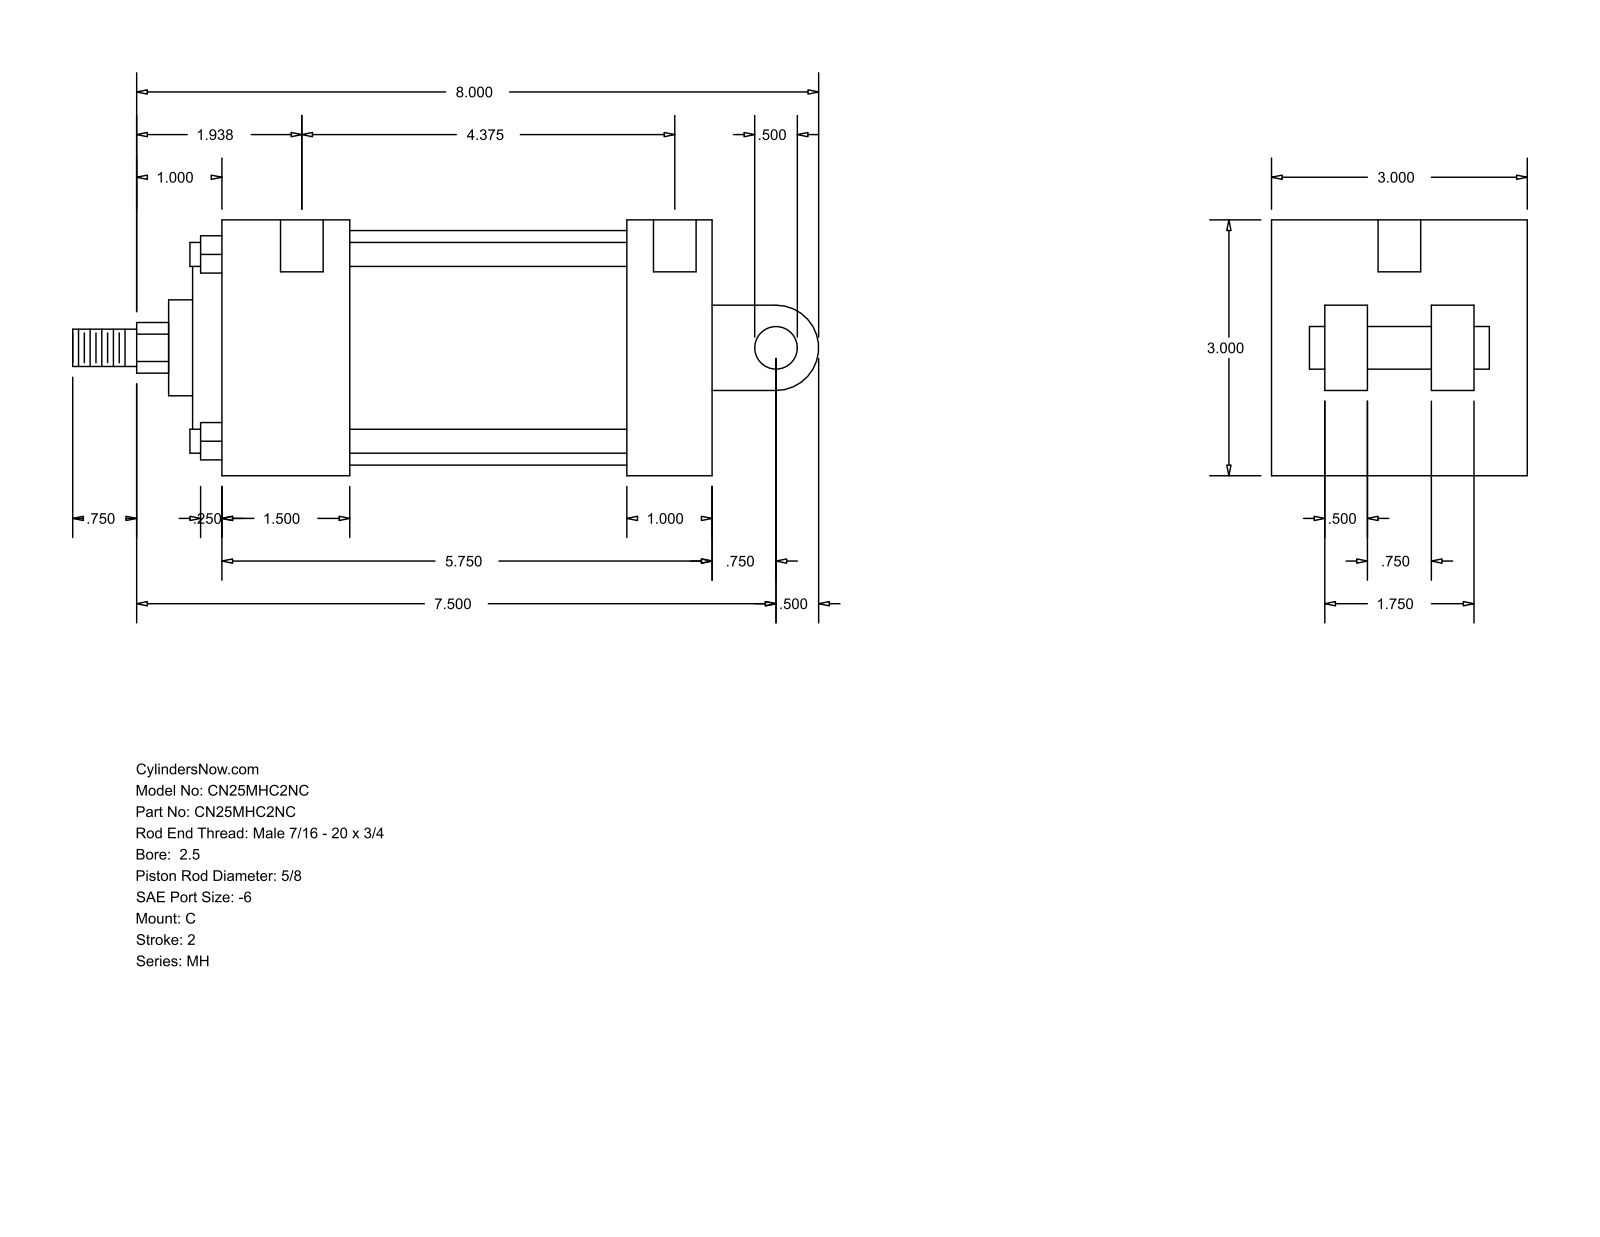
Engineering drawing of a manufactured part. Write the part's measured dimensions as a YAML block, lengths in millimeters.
part_name: "MH_C__0250_0.625"
step_written_by: "GSSL Pune (CONFIG_CONTROL_DESIGN)"
units: millimeters
bodies: {solids: 0, faces: 101, planar: 71, cylindrical: 30, other: 0}
overall_size: [222.25, 76.2, 76.2]
round_holes:
  - {diameter: 5.56, count: 4}
  - {diameter: 12.7, count: 2}
round_bosses_or_shafts:
  - {diameter: 7.14, count: 4}
  - {diameter: 69.85, count: 1}
  - {diameter: 55.55, count: 1}
  - {diameter: 28.57, count: 1}
  - {diameter: 15.88, count: 1}
  - {diameter: 12.7, count: 1}
  - {diameter: 11.11, count: 1}
partial_cylinders:
  - {radius: 7.54, count: 1}
  - {radius: 12.7, count: 1}
face_to_face_distances: [76.2, 25.4, 146.05, 15.87, 38.1, 82.55, 120.65, 107.95, 8.73, 46.83]
hole_center_spacings: [119.06, 3.17, 4.76, 111.13, 114.3, 115.89]
